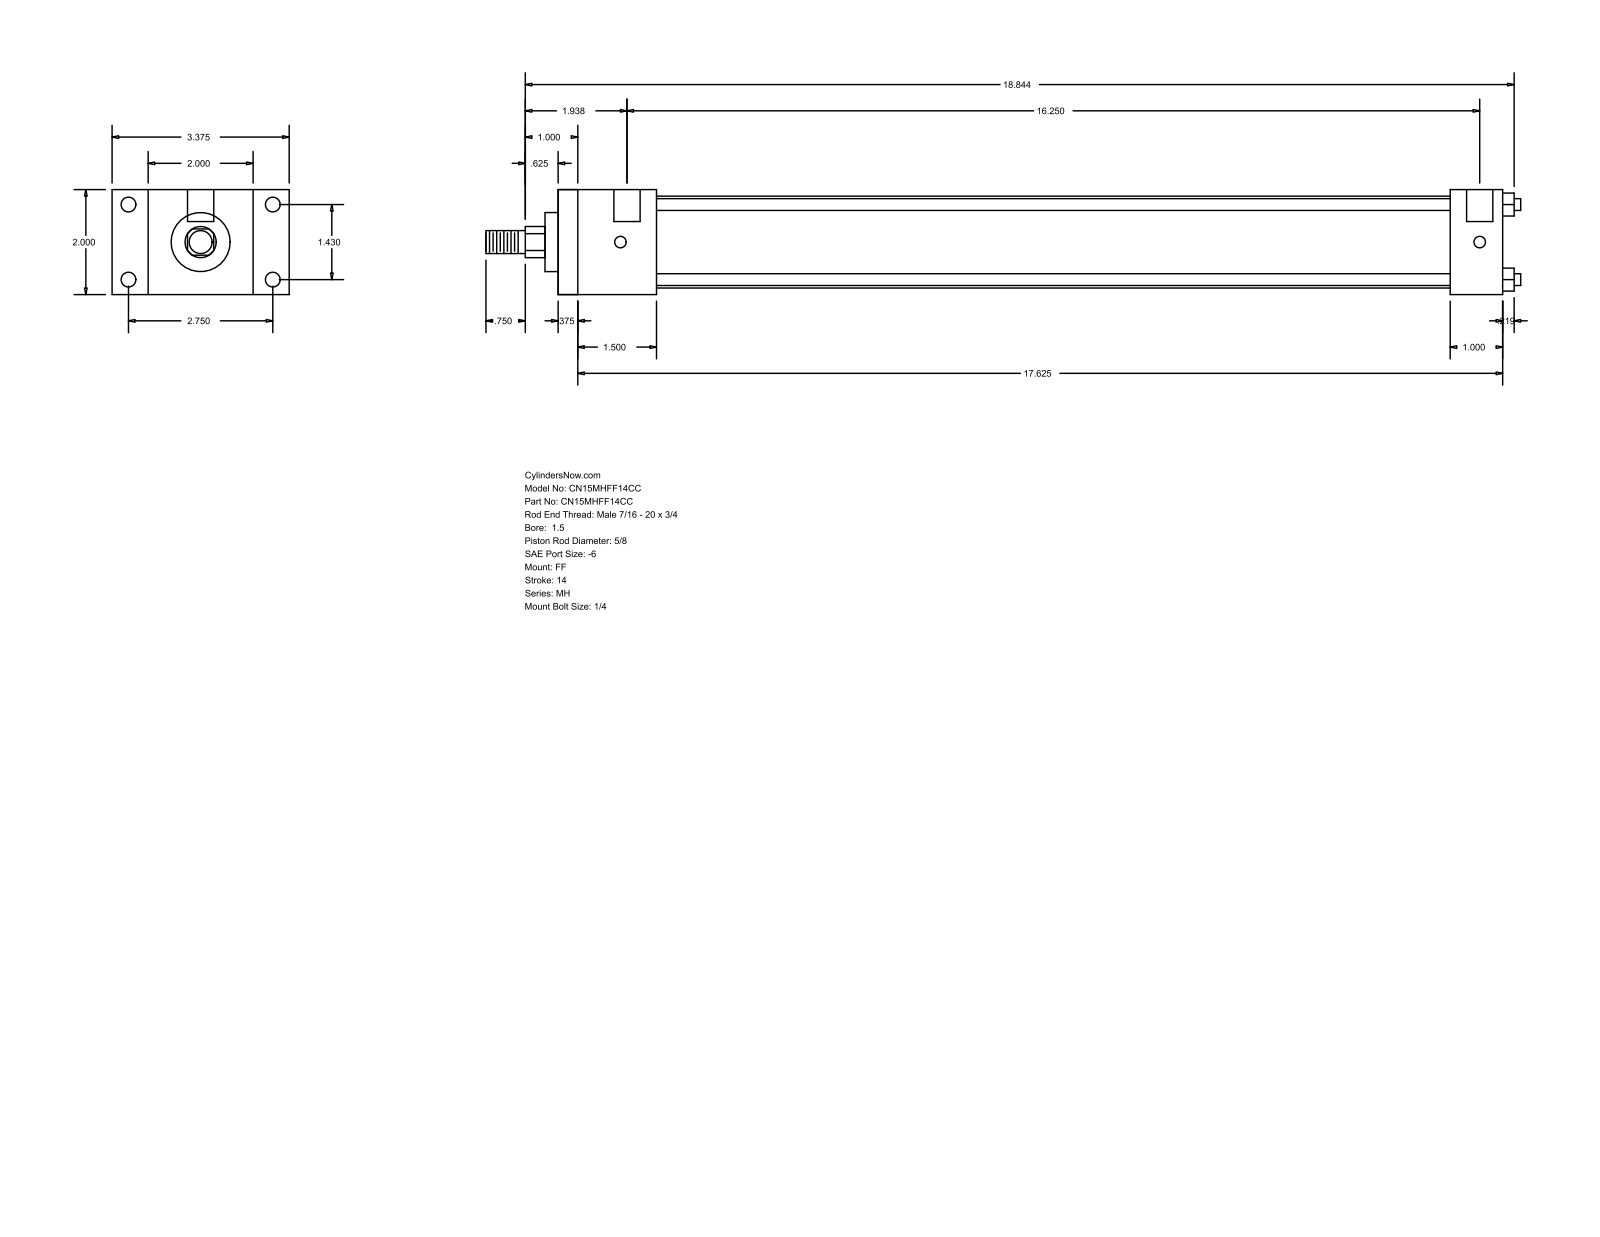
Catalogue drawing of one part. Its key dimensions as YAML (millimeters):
part_name: "MH_FF__0150_0.625"
step_written_by: "GSSL Pune (CONFIG_CONTROL_DESIGN)"
units: millimeters
bodies: {solids: 0, faces: 92, planar: 64, cylindrical: 28, other: 0}
overall_size: [500.86, 85.72, 50.8]
round_holes:
  - {diameter: 5.56, count: 4}
  - {diameter: 7.14, count: 4}
  - {diameter: 12.7, count: 2}
round_bosses_or_shafts:
  - {diameter: 5.71, count: 4}
  - {diameter: 44.45, count: 1}
  - {diameter: 28.57, count: 1}
  - {diameter: 15.88, count: 1}
  - {diameter: 11.11, count: 1}
partial_cylinders:
  - {radius: 7.54, count: 1}
face_to_face_distances: [50.8, 457.19, 9.52, 447.67, 17.46, 68.26, 47.62, 38.1, 409.57, 431.8]
hole_center_spacings: [36.32, 69.84, 78.72, 415.92, 3.17, 412.75]
